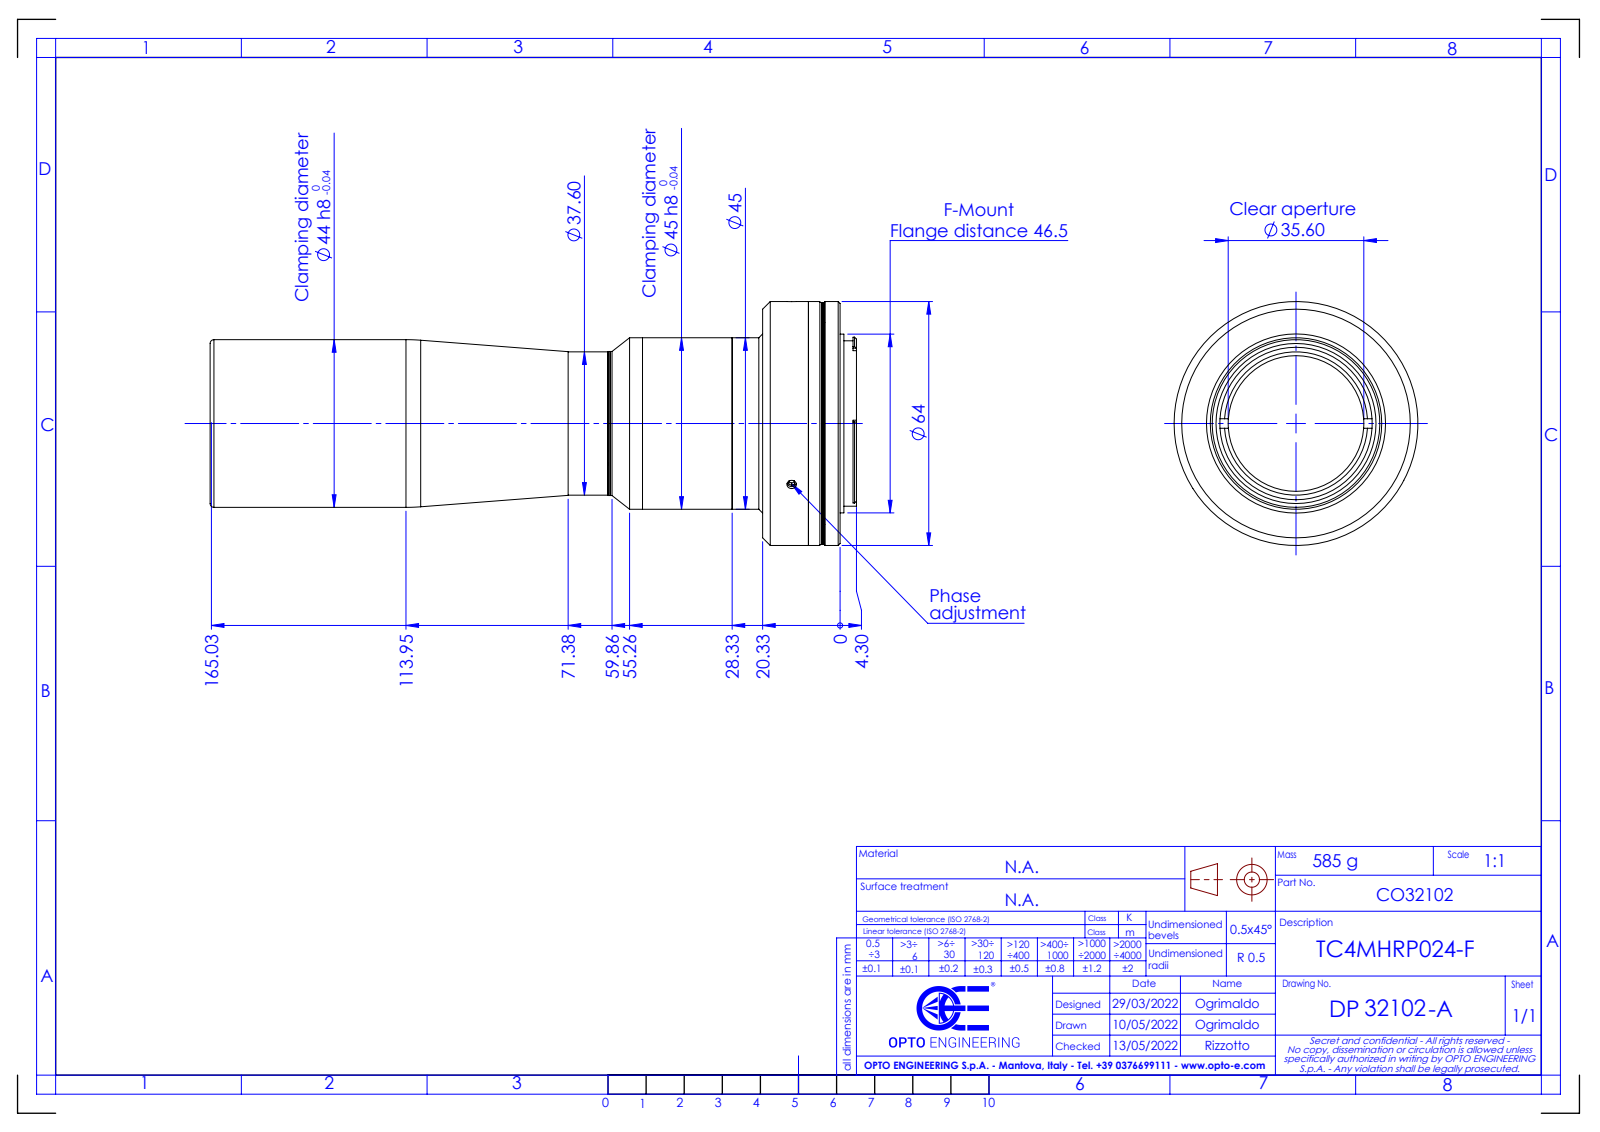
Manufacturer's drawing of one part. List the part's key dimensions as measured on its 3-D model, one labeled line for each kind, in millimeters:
Part name (STEP PRODUCT): DP32102-A_TC4MHRP024-F
STEP written by: SolidWorks 2021 (CONFIG_CONTROL_DESIGN)
Units: millimetres
Bodies: 0 solids, 151 faces (54 planar, 63 cylindrical, 34 other)
Overall size (bounding box): 169.66 × 64 × 64
Round holes (diameter × count): ⌀2.5 ×3, ⌀29 ×1, ⌀32 ×1, ⌀35.6 ×1, ⌀40 ×1, ⌀42 ×1
Round bosses / shafts (diameter × count): ⌀64 ×1, ⌀63.5 ×1, ⌀46.9 ×1, ⌀45 ×1, ⌀44 ×1, ⌀43.4 ×1, ⌀37.8 ×1, ⌀37.6 ×1
Partial cylindrical surfaces — rounded edges, fillets, slot ends (radius × count): R0.5 ×6, R1.15 ×2, R22.65 ×1
Main face-to-face distances: 0.5, 8.3, 3, 4.3, 5.3, 12.02, 15.02, 20.32, 16.32, 1.3
